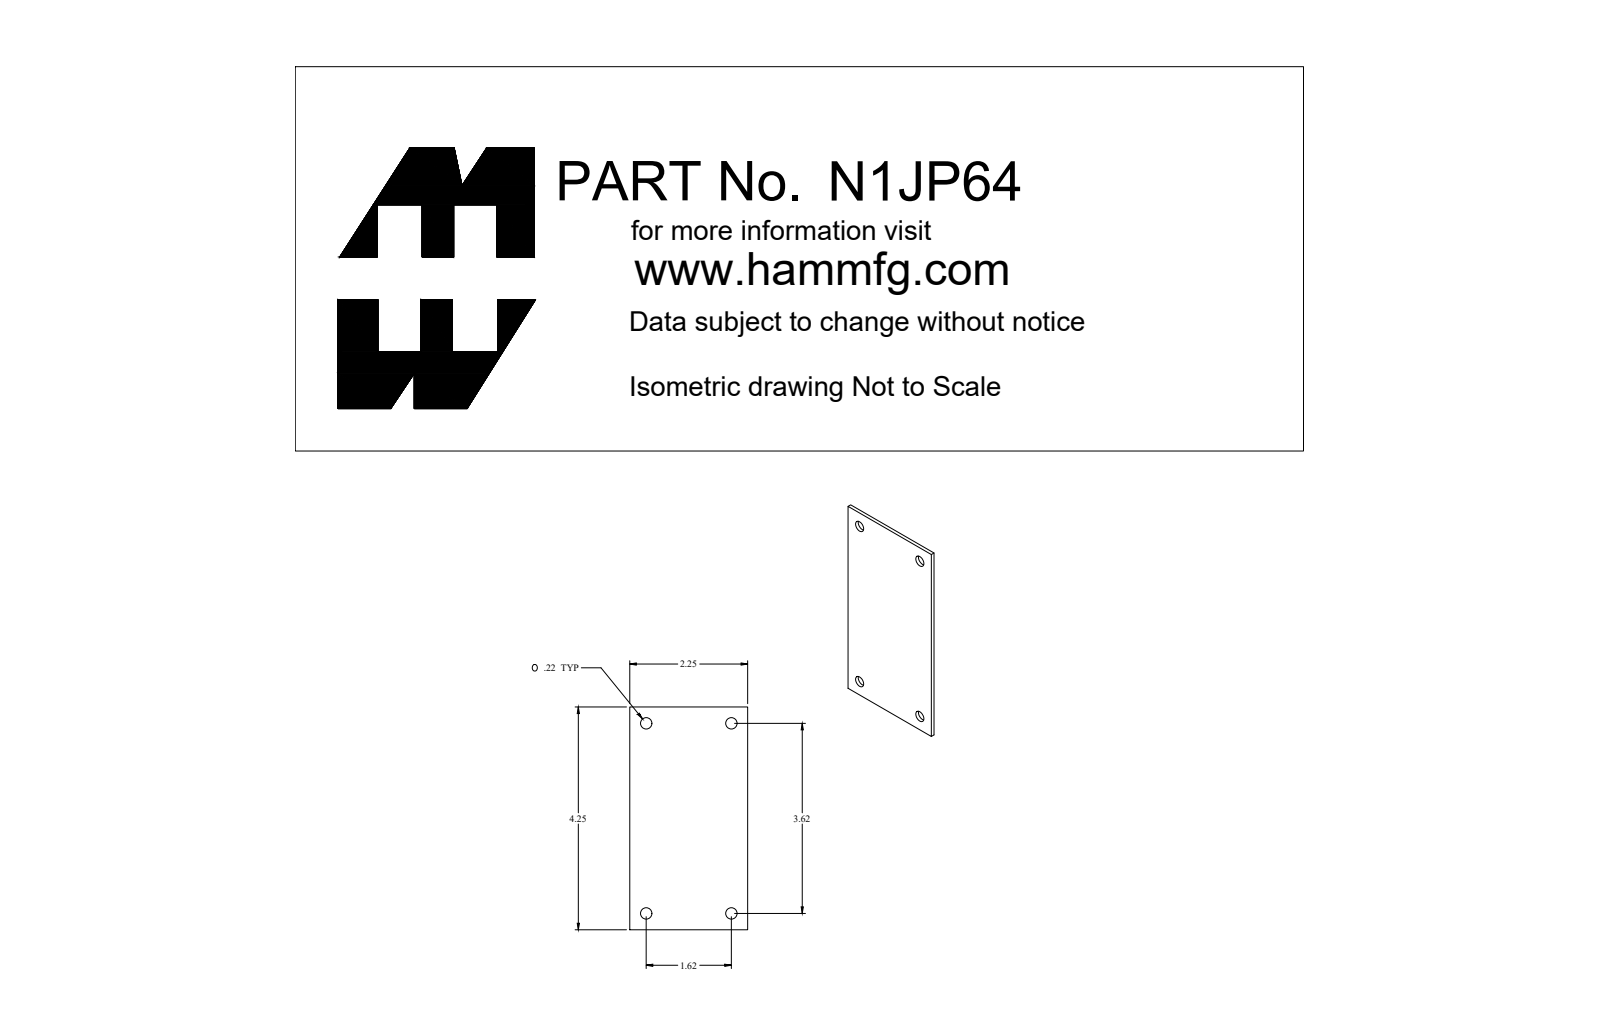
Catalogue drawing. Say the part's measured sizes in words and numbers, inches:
The part is named "N1JP64". Its 3-D file was written by "SolidWorks 2018 (AUTOMOTIVE_DESIGN)". It is 1 solid with 18 faces: 6 planar, 12 cylindrical and 0 other. Overall it measures 4.25 by 2.25 by 0.072 inches. Its volume is 0.672 cubic inches and its surface area 19.82 square inches. Round holes: 4 of diameter 0.265. Partial cylindrical surfaces (rounded edges, fillets, slot ends): 4 of radius 0.125. The main face-to-face distances are 0.072, 2.25, 4.25. The hole center spacings are 1.625, 3.625, 3.972.
